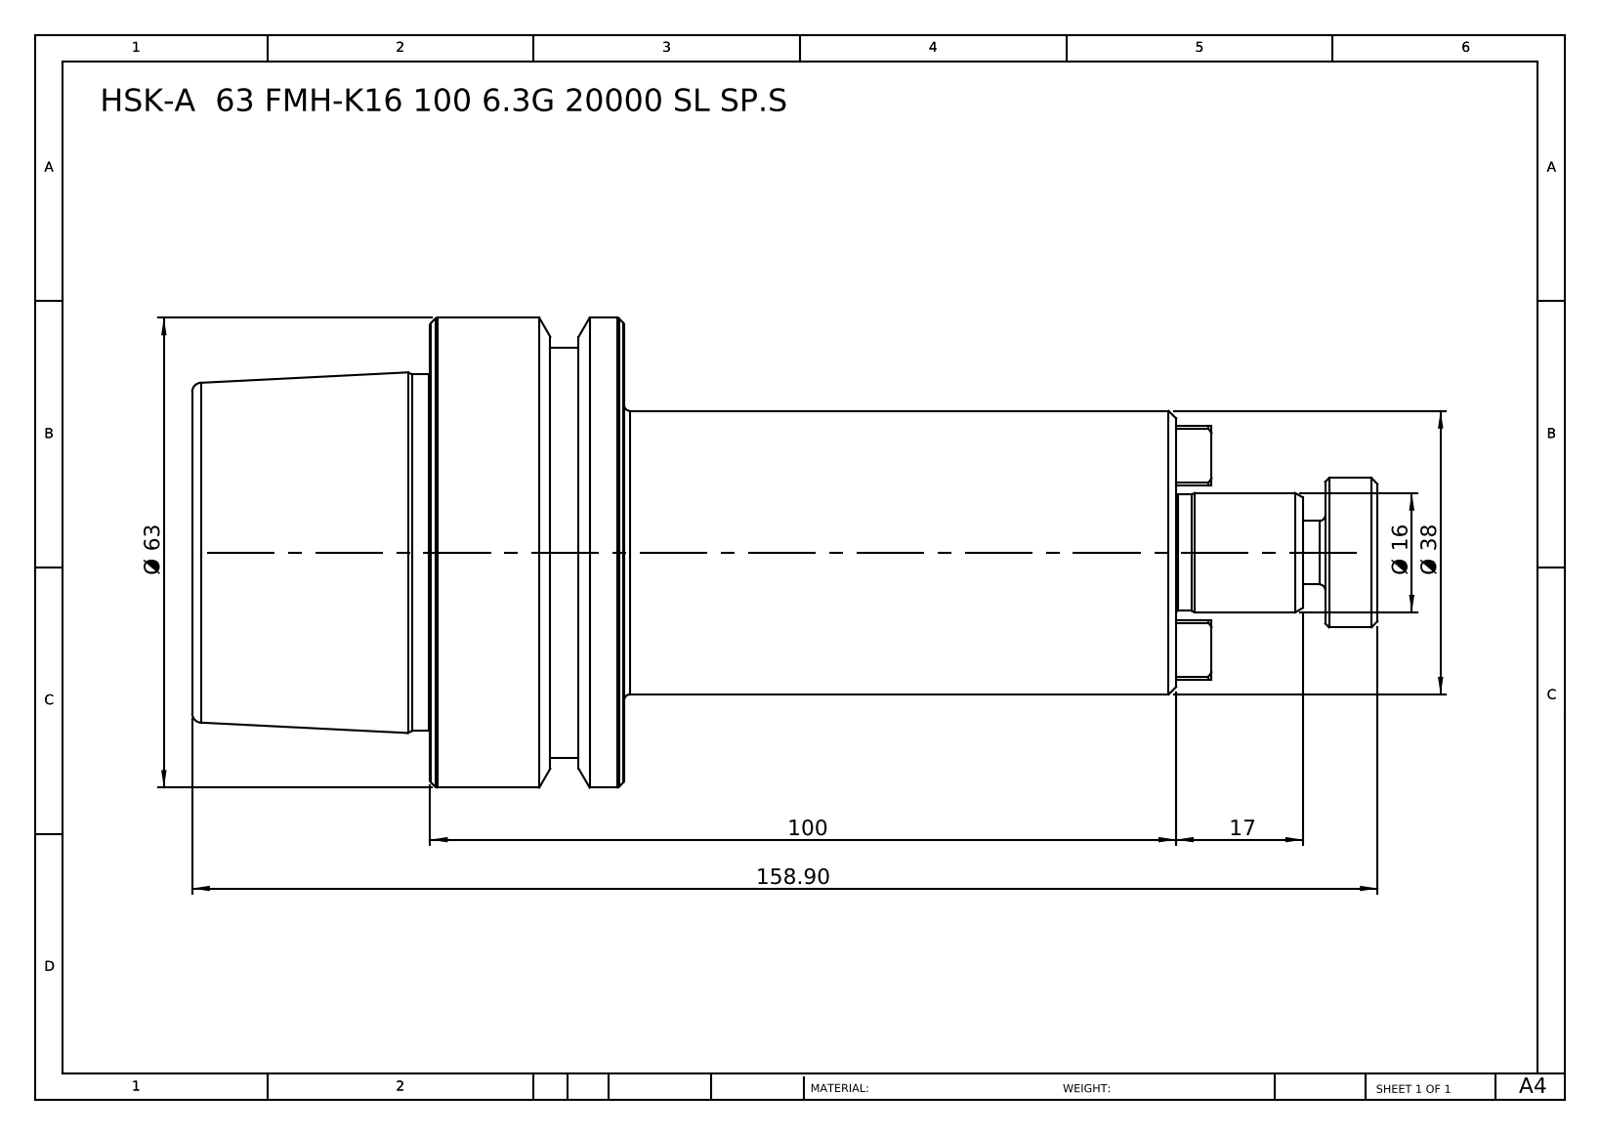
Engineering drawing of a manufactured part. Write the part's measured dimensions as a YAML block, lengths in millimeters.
part_name: "HSK-A 63 FMH16 100 6.3G 20000 SL SP.S"
step_written_by: "SolidWorks 2014 (CONFIG_CONTROL_DESIGN)"
units: millimeters
bodies: {solids: 1, faces: 99, planar: 37, cylindrical: 18, other: 44}
overall_size: [158.9, 63, 63]
volume: 222775
surface_area: 27488
round_bosses_or_shafts:
  - {diameter: 63, count: 1}
  - {diameter: 55, count: 1}
  - {diameter: 47.78, count: 1}
  - {diameter: 38, count: 1}
  - {diameter: 20, count: 1}
  - {diameter: 16, count: 1}
  - {diameter: 15.6, count: 1}
  - {diameter: 8.5, count: 1}
face_to_face_distances: [57.9, 26, 31.9, 74, 100, 131.9, 27, 101, 127, 158.9]
